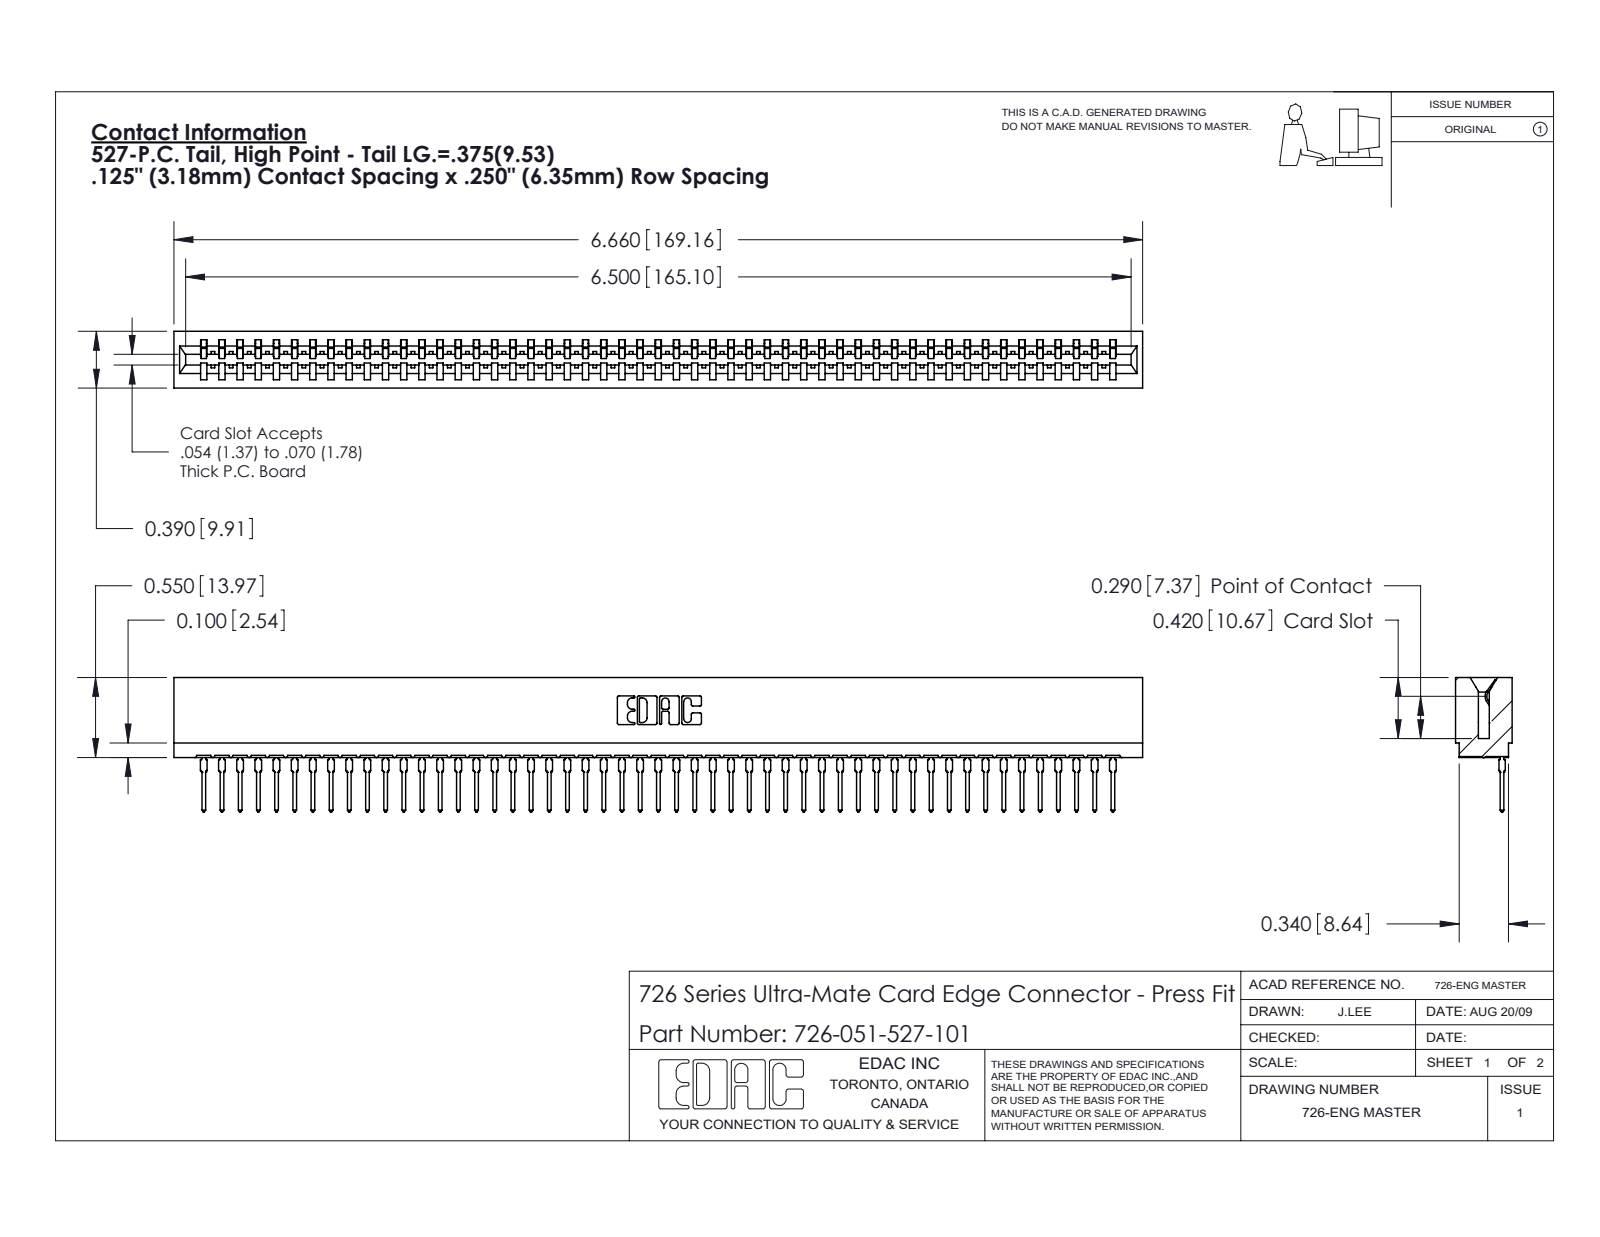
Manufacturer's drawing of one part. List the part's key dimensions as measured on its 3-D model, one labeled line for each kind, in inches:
Part name (STEP PRODUCT): 726-051-527-101; 726 Part_.515 Slot Depth - 01; 746-292-001_527
STEP written by: SolidWorks 2020 (CONFIG_CONTROL_DESIGN)
Units: inches
Bodies: 52 solids, 5605 faces (3268 planar, 1011 cylindrical, 1326 other)
Overall size (bounding box): 6.66 × 0.924 × 0.39
Volume: 0.922 in³ · Surface area: 36.38 in²
Partial cylindrical surfaces — rounded edges, fillets, slot ends (radius × count): R0.021 ×102, R0.015 ×52, R0.01 ×22, R0.007 ×6, R0.031 ×6, R0.005 ×4, R0.011 ×4, R0.026 ×3
Main face-to-face distances: 0.057, 0.333, 0.39, 0.025, 0.307, 0.25, 0.275, 0.083, 0.365, 0.032
